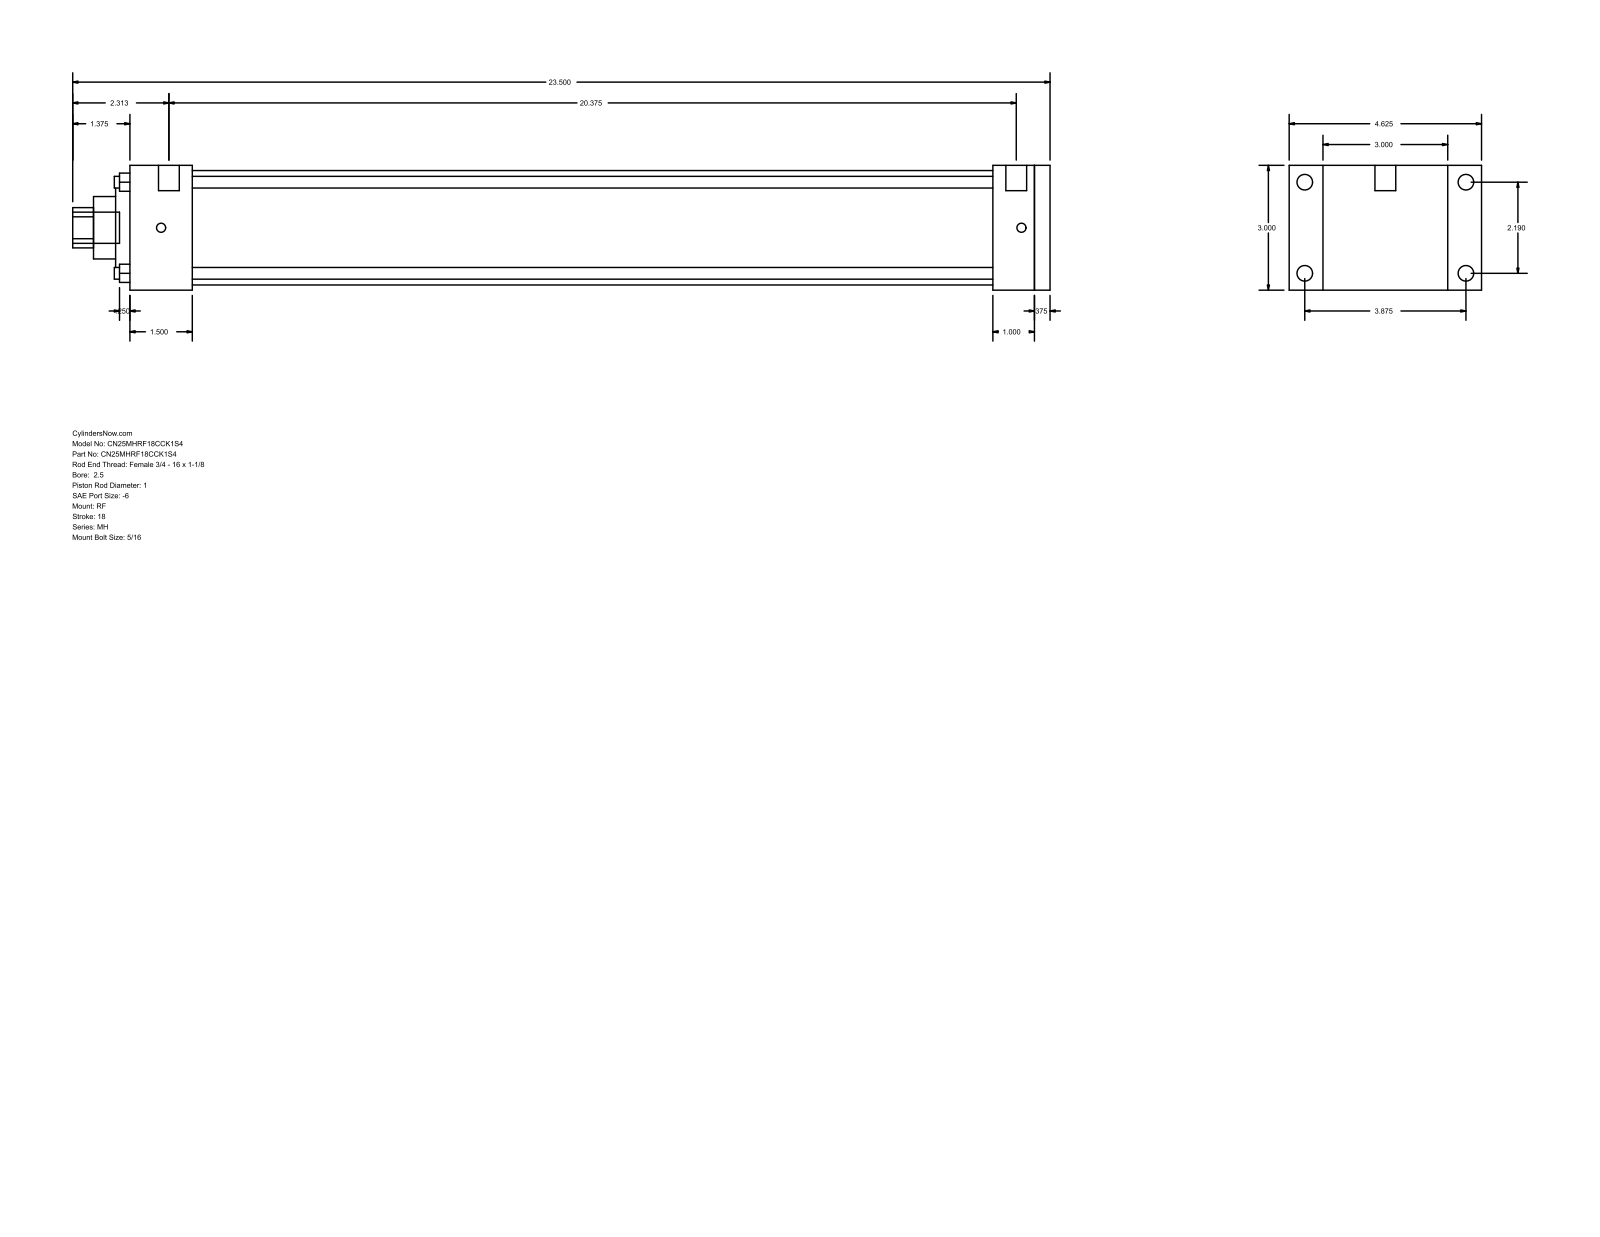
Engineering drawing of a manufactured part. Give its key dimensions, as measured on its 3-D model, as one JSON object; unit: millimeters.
{"part_name": "MH_RF__0250_1", "step_written_by": "GSSL Pune (CONFIG_CONTROL_DESIGN)", "units": "millimeters", "bodies": {"solids": 0, "faces": 94, "planar": 65, "cylindrical": 29, "other": 0}, "overall_size": [596.9, 117.47, 76.2], "round_holes": [[7.14, 4], [25.4, 1], [38.1, 1], [60.33, 1], [69.85, 1]], "round_bosses_or_shafts": [[9.53, 4], [5.56, 4], [12.7, 2], [19.05, 1]], "partial_cylinders_radius": [[12.29, 1]], "face_to_face_distances": [76.2, 9.52, 561.98, 552.46, 25.4, 34.92, 527.06, 38.11, 488.95, 514.35], "hole_center_spacings": [39.33, 55.62, 78.66]}
